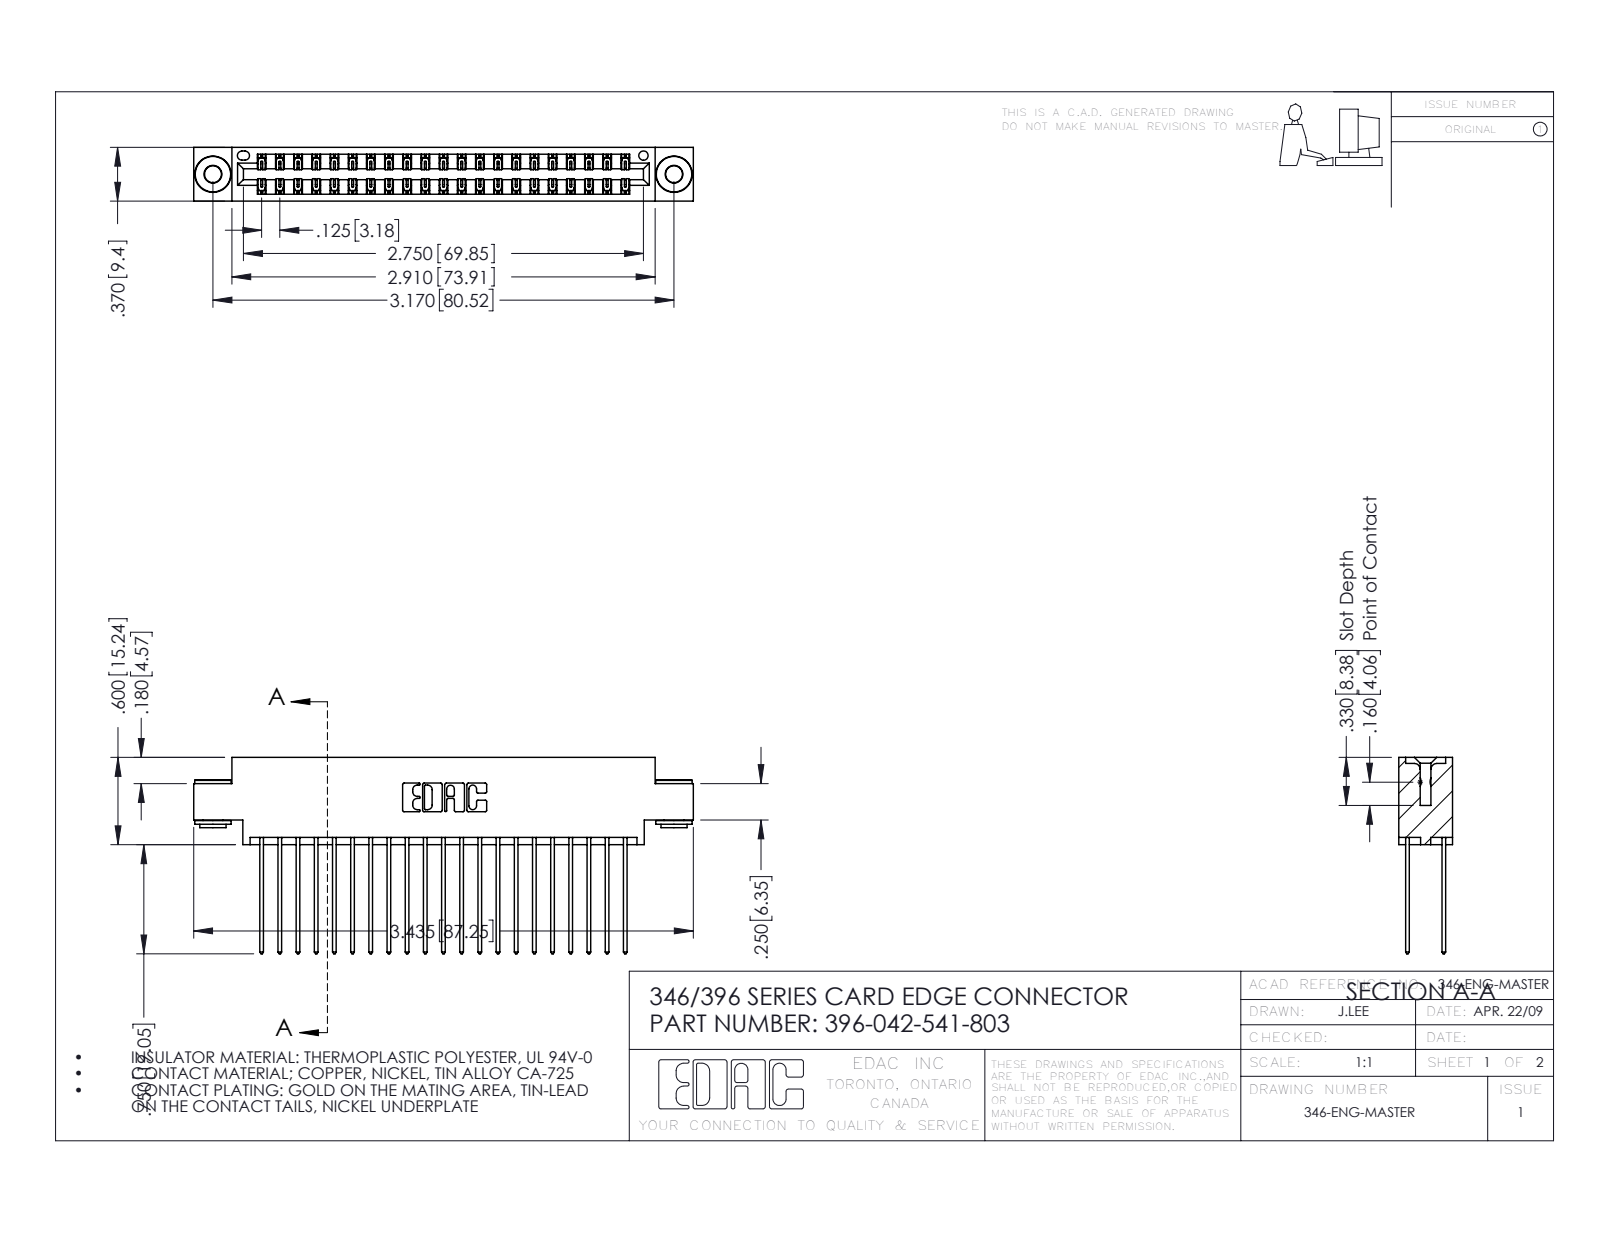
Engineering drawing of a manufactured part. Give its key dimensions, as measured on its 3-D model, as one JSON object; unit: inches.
{"part_name": "345-292-001_345-293-141; 396-042-541-803; 346 Part_0.170 Offset - 0.156 Dia-TH; 345-250-002_345-250-002-102", "step_written_by": "SolidWorks 2016 (CONFIG_CONTROL_DESIGN)", "units": "inches", "bodies": {"solids": 45, "faces": 2348, "planar": 1560, "cylindrical": 780, "other": 8}, "overall_size": [3.435, 1.35, 0.37], "volume_in3": 0.516, "surface_area_in2": 19.89, "round_holes": [[0.116, 2], [0.156, 2], [0.064, 1]], "round_bosses_or_shafts": [[0.25, 2], [0.18, 2], [0.136, 2]], "partial_cylinders_radius": [[0.006, 63], [0.01, 42], [0.01, 22], [0.007, 6], [0.031, 6], [0.026, 3], [0.014, 2], [0.022, 2]], "face_to_face_distances": [0.048, 0.322, 0.25, 0.025, 0.37, 0.072, 0.298, 0.275, 0.225, 0.148], "hole_center_spacings": [0.246, 2.963, 3.17]}
